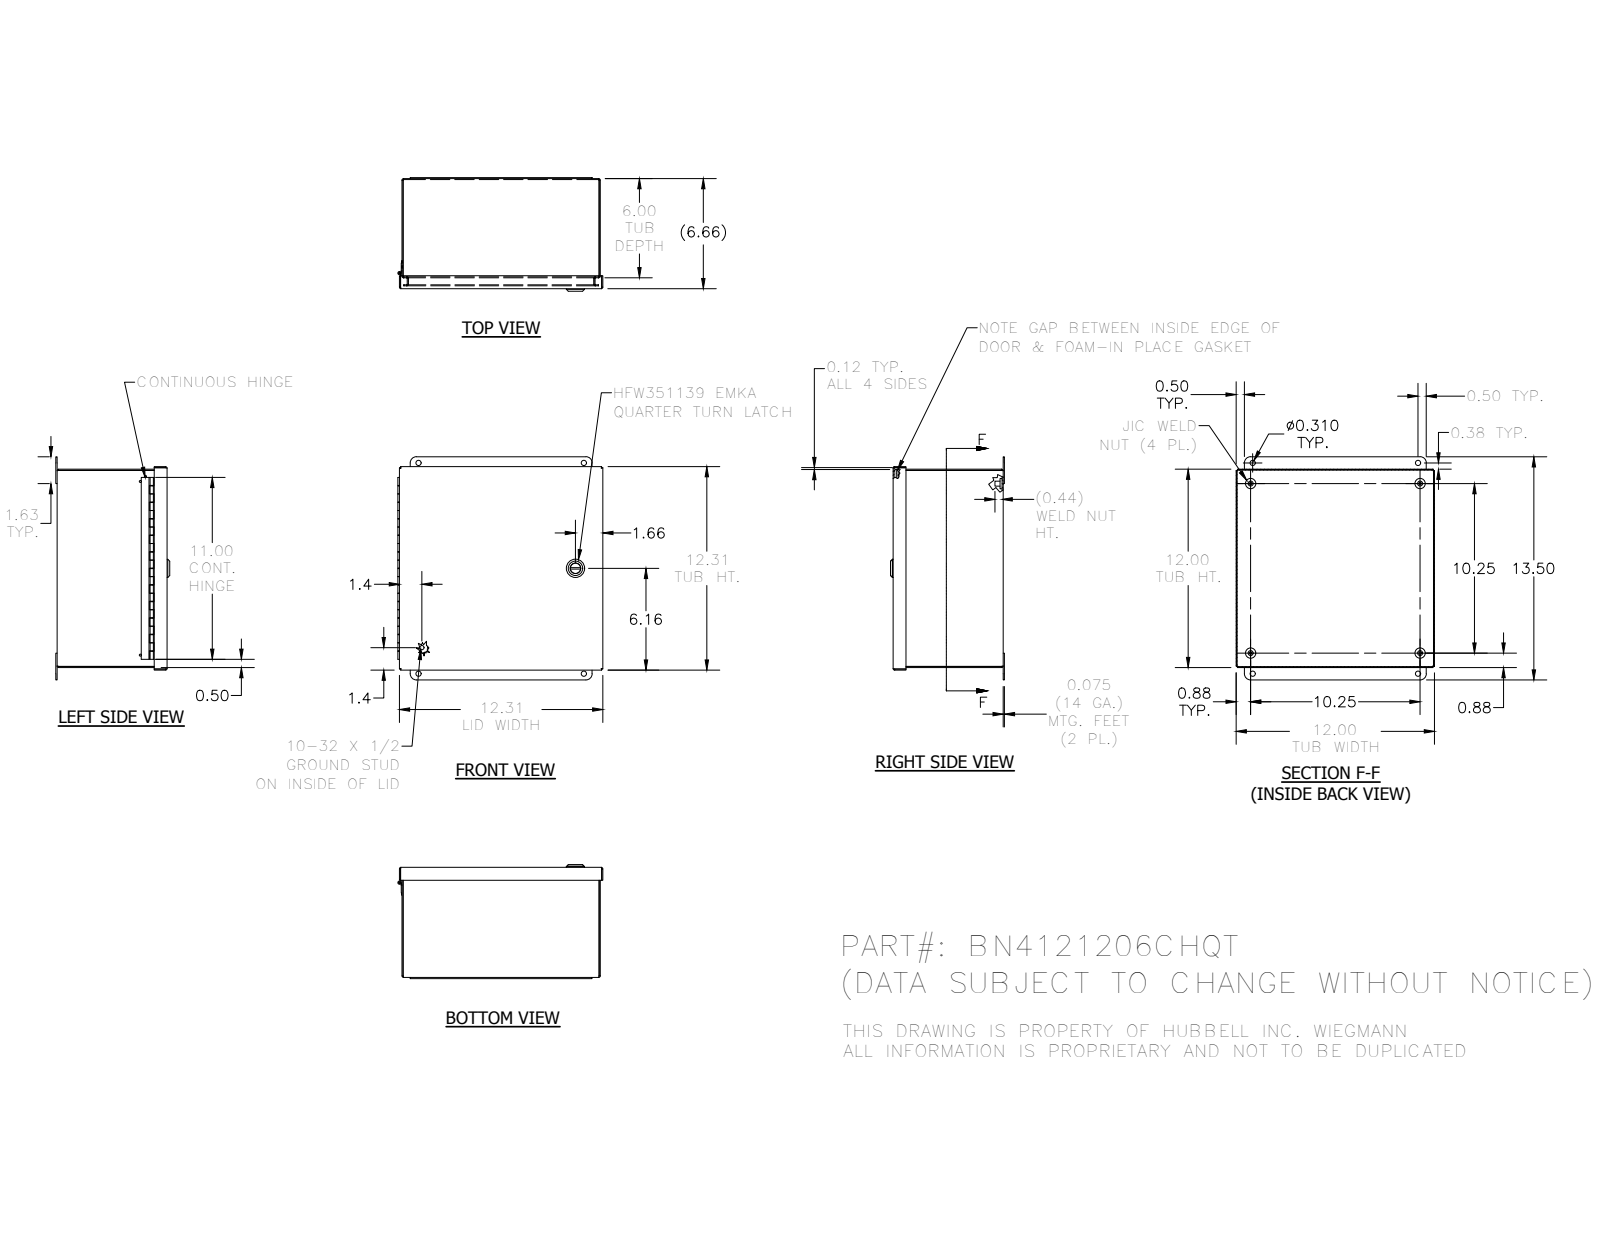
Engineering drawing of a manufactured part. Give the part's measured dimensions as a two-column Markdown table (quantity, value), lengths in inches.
| quantity | value |
| --- | --- |
| part name | BN4121206CHQT |
| STEP written by | SolidWorks 2018 (AUTOMOTIVE_DESIGN) |
| units | inches |
| bodies | 21 solids, 785 faces (396 planar, 261 cylindrical, 128 other) |
| overall size | 13.5 × 12.406 × 6.888 |
| volume | 49.36 in³ |
| surface area | 1 509 in² |
| round holes (diameter × count) | 0.156 × 4, 0.31 × 4, 0.12 × 3, 0.116 × 1, 0.197 × 1, 0.315 × 1, 0.394 × 1, 0.402 × 1, 0.634 × 1, 0.802 × 1 |
| round bosses / shafts (diameter × count) | 0.625 × 4, 0.3 × 4, 1.102 × 1, 0.866 × 1, 0.78 × 1, 0.622 × 1, 0.598 × 1, 0.531 × 1 |
| partial cylindrical surfaces (radius × count) | 0.012 × 30, 0.031 × 20, 0.093 × 20, 0.125 × 16, 0.02 × 12, 0.157 × 4, 0.375 × 4, 0.016 × 2 |
| main face-to-face distances | 0.062, 0.062, 11.938, 6.594, 6.656, 6.532, 6.594, 12, 11.876, 11.938 |
| hole center spacings | 10.25, 15.322, 1.256, 10, 10.202, 10.202, 10.9, 11.501 |
